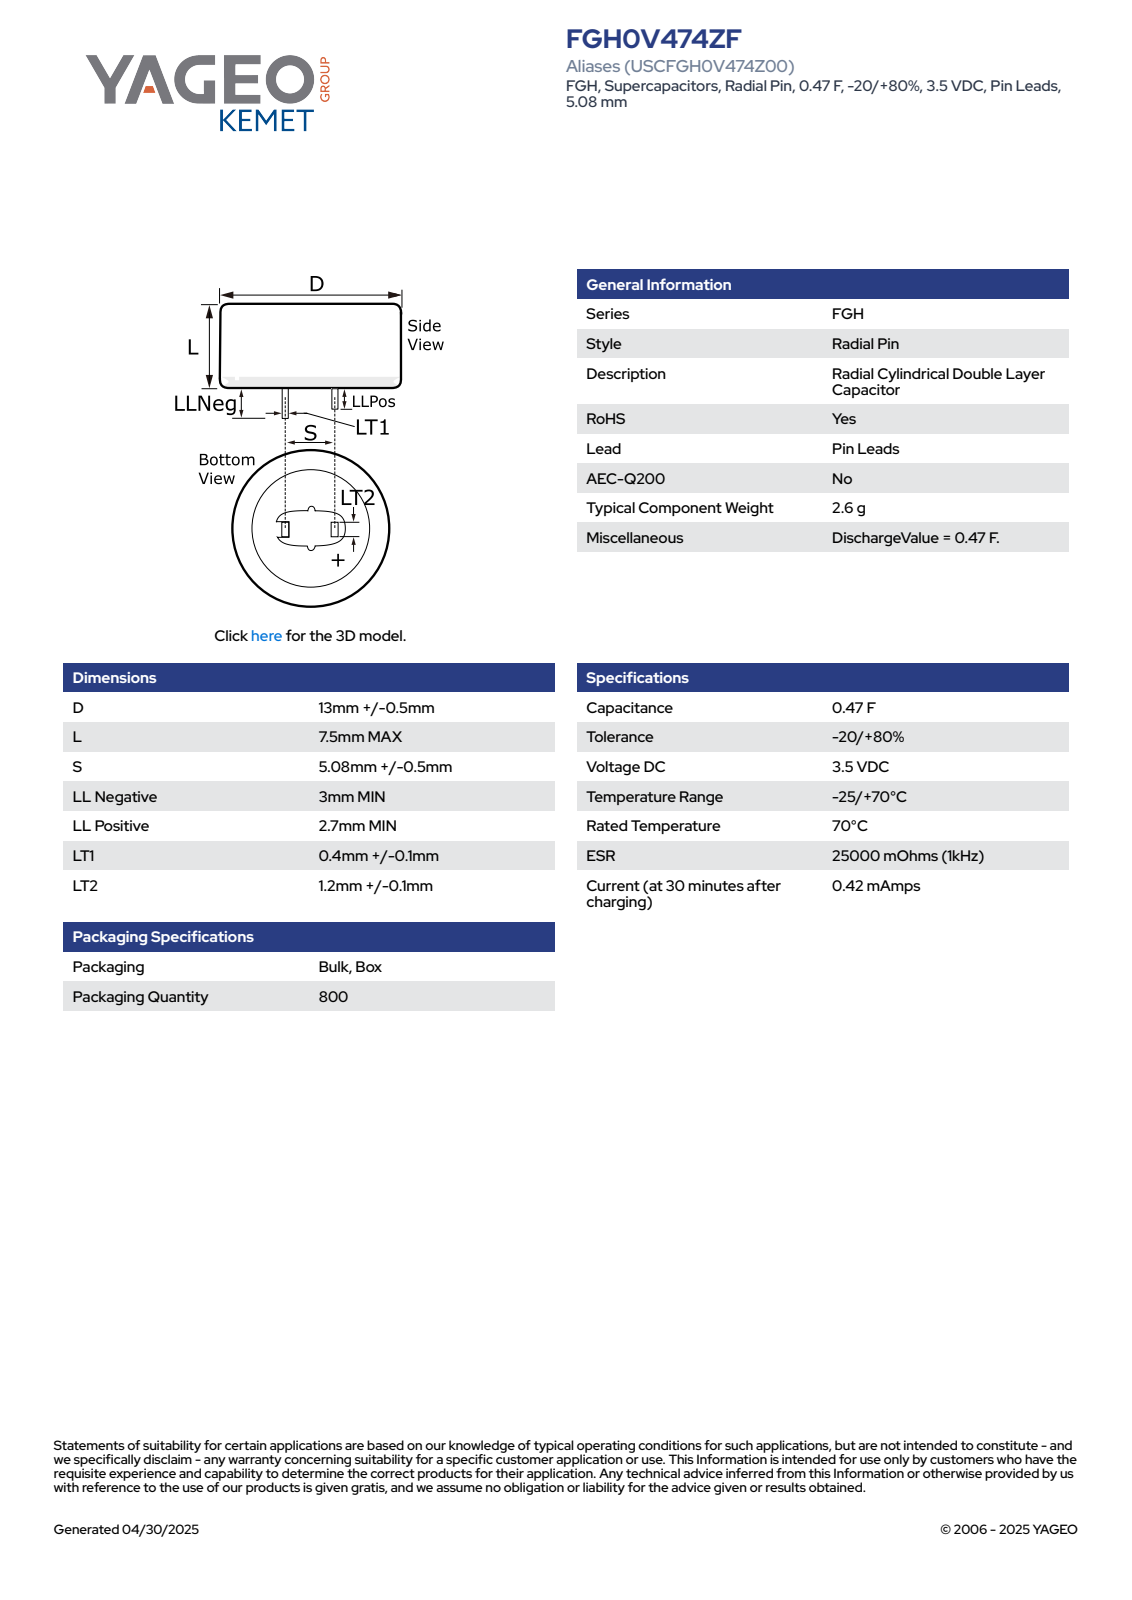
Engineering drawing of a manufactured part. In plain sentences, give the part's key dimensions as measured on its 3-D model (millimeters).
The part is named "CDR_LPLLN_D13.5L7.5S5.08LLNEG3LLPOS2.7LT10.5LT21.3". Its 3-D file was written by "SolidWorks 2014 (AUTOMOTIVE_DESIGN)". It is 1 solid with 78 faces: 70 planar, 4 cylindrical and 4 other. Overall it measures 13.5 by 13.5 by 10.5 millimeters. Its volume is 1 073 cubic millimeters and its surface area 608 square millimeters. Round bosses or shafts: 1 of diameter 13.5. Partial cylindrical surfaces (rounded edges, fillets, slot ends): 1 of radius 6.76. The main face-to-face distances are 7.5, 0.5, 5.08, 5.58, 4.58, 1.3, 2.7, 10.2, 3, 10.5.
